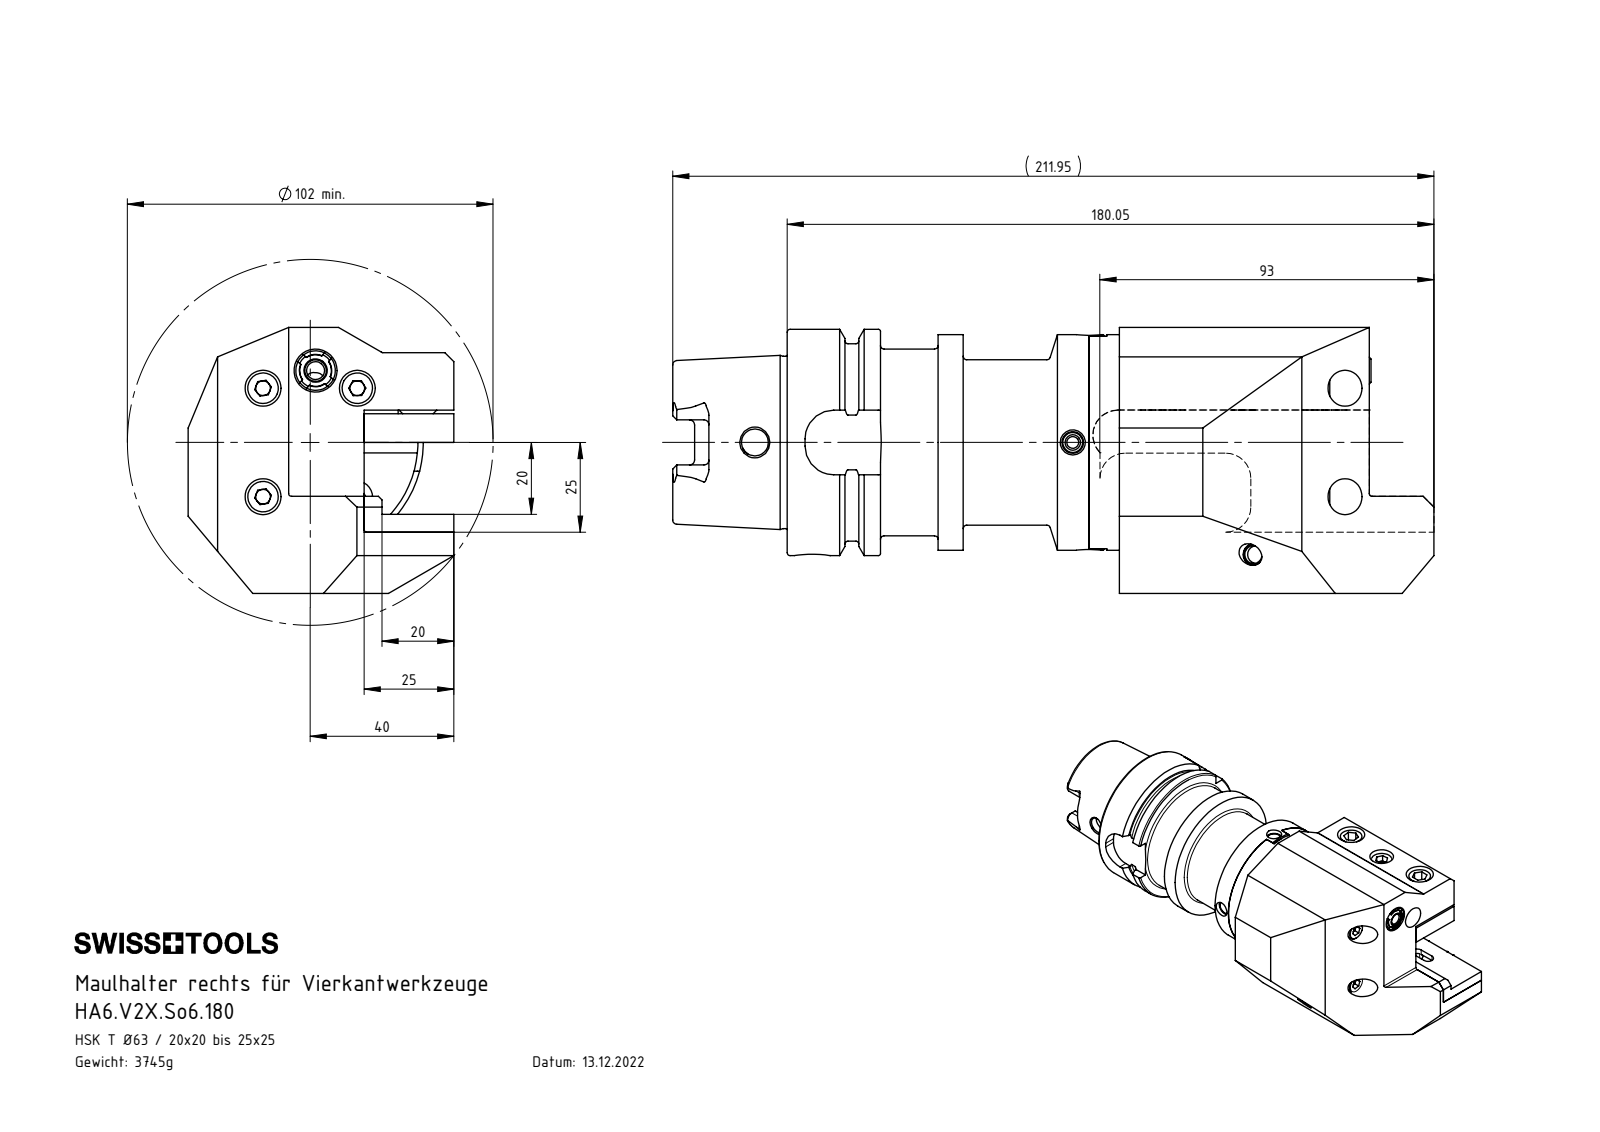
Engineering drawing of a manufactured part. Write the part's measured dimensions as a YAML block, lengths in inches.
part_name: "ISO 8735 - 6x16; So6-V2X.R11.093_A_Stiftbohrungen; V2X-ER1.025.066_A; KU1-010.010.030_A (+8 more)"
step_written_by: "SolidWorks 2017 (AUTOMOTIVE_DESIGN)"
units: inches
bodies: {solids: 28, faces: 930, planar: 310, cylindrical: 258, other: 362}
overall_size: [8.344, 2.913, 2.913]
volume: 29.47
surface_area: 168.3
round_holes:
  - {diameter: 0.197, count: 9}
  - {diameter: 0.394, count: 6}
  - {diameter: 0.165, count: 5}
  - {diameter: 0.236, count: 5}
  - {diameter: 0.217, count: 4}
  - {diameter: 0.13, count: 2}
  - {diameter: 0.169, count: 2}
  - {diameter: 0.276, count: 2}
  - {diameter: 0.402, count: 2}
  - {diameter: 0.433, count: 2}
  - {diameter: 0.157, count: 1}
  - {diameter: 0.268, count: 1}
round_bosses_or_shafts:
  - {diameter: 0.472, count: 4}
  - {diameter: 0.335, count: 4}
  - {diameter: 0.197, count: 4}
  - {diameter: 0.236, count: 3}
  - {diameter: 2.48, count: 1}
  - {diameter: 2.362, count: 1}
  - {diameter: 2.163, count: 1}
  - {diameter: 2.047, count: 1}
partial_cylinders:
  - {radius: 0.055, count: 6}
  - {radius: 0.276, count: 5}
  - {radius: 0.113, count: 4}
  - {radius: 0.13, count: 4}
  - {radius: 0.315, count: 4}
  - {radius: 0.031, count: 2}
  - {radius: 0.098, count: 2}
  - {radius: 0.236, count: 2}
face_to_face_distances: [0.984, 0.669, 0.866, 0.197, 1.969, 1.299, 0.315, 1.654, 0.787, 0.335]
hole_center_spacings: [0.787, 0.891, 1.033, 1.188, 1.574, 0.059, 0.496, 0.607]
